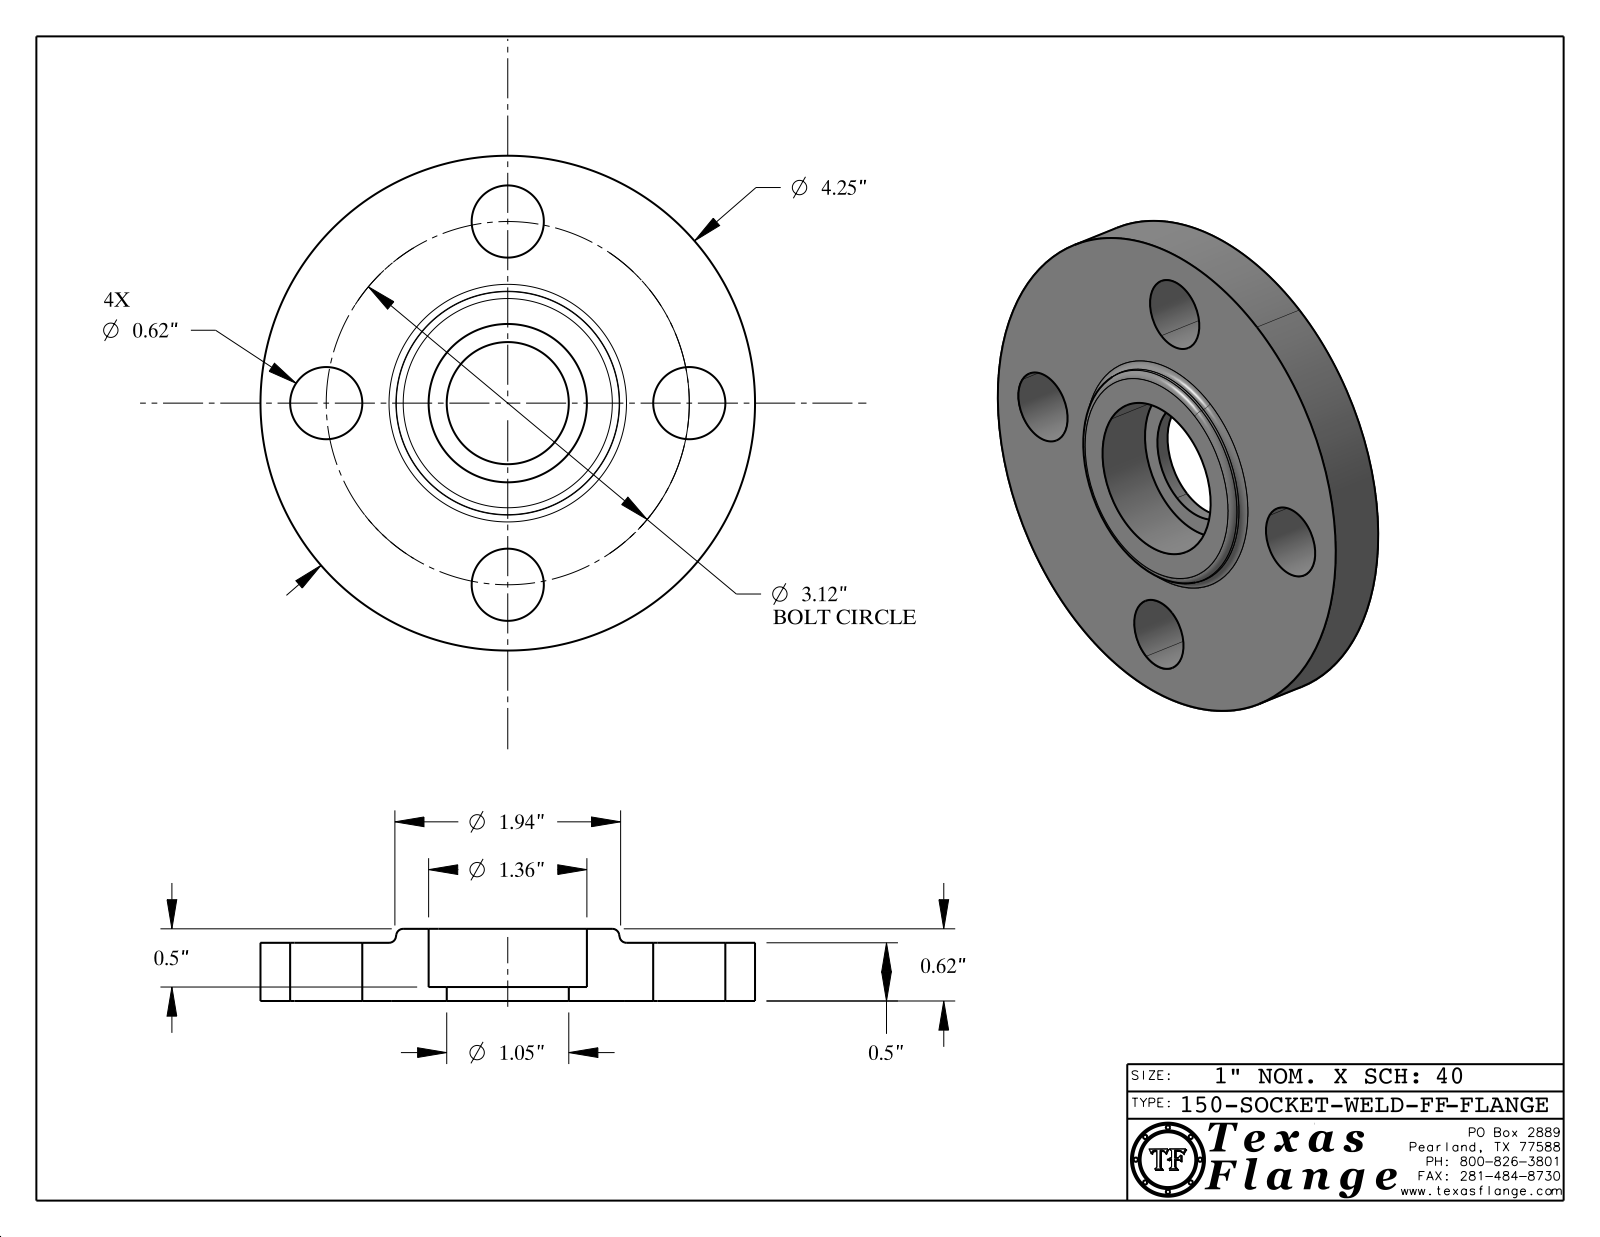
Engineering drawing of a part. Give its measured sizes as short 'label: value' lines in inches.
name: 150-SOCKET-WELD-FF
written by: CATIA V5 STEP AP214 (AUTOMOTIVE_DESIGN)
unit: in
bodies: 1 solid, 410 faces (370 planar, 34 cylindrical, 6 other)
size: 4.25 × 4.25 × 0.62
volume: 6.005 in³; area: 37.83 in²
holes: 4× ⌀0.62, 1× ⌀0.495, 1× ⌀1.049, 1× ⌀1.36
bosses: 8× ⌀0.03, 1× ⌀4.25, 1× ⌀0.39
face distances: 0.5, 0.12, 0.62, 0.38, 0.485, 0.365, 0.015, 0.135, 0.148, 0.144
hole spacings: 1.56, 2.206, 1.194, 2.882, 3.12, 1.56
